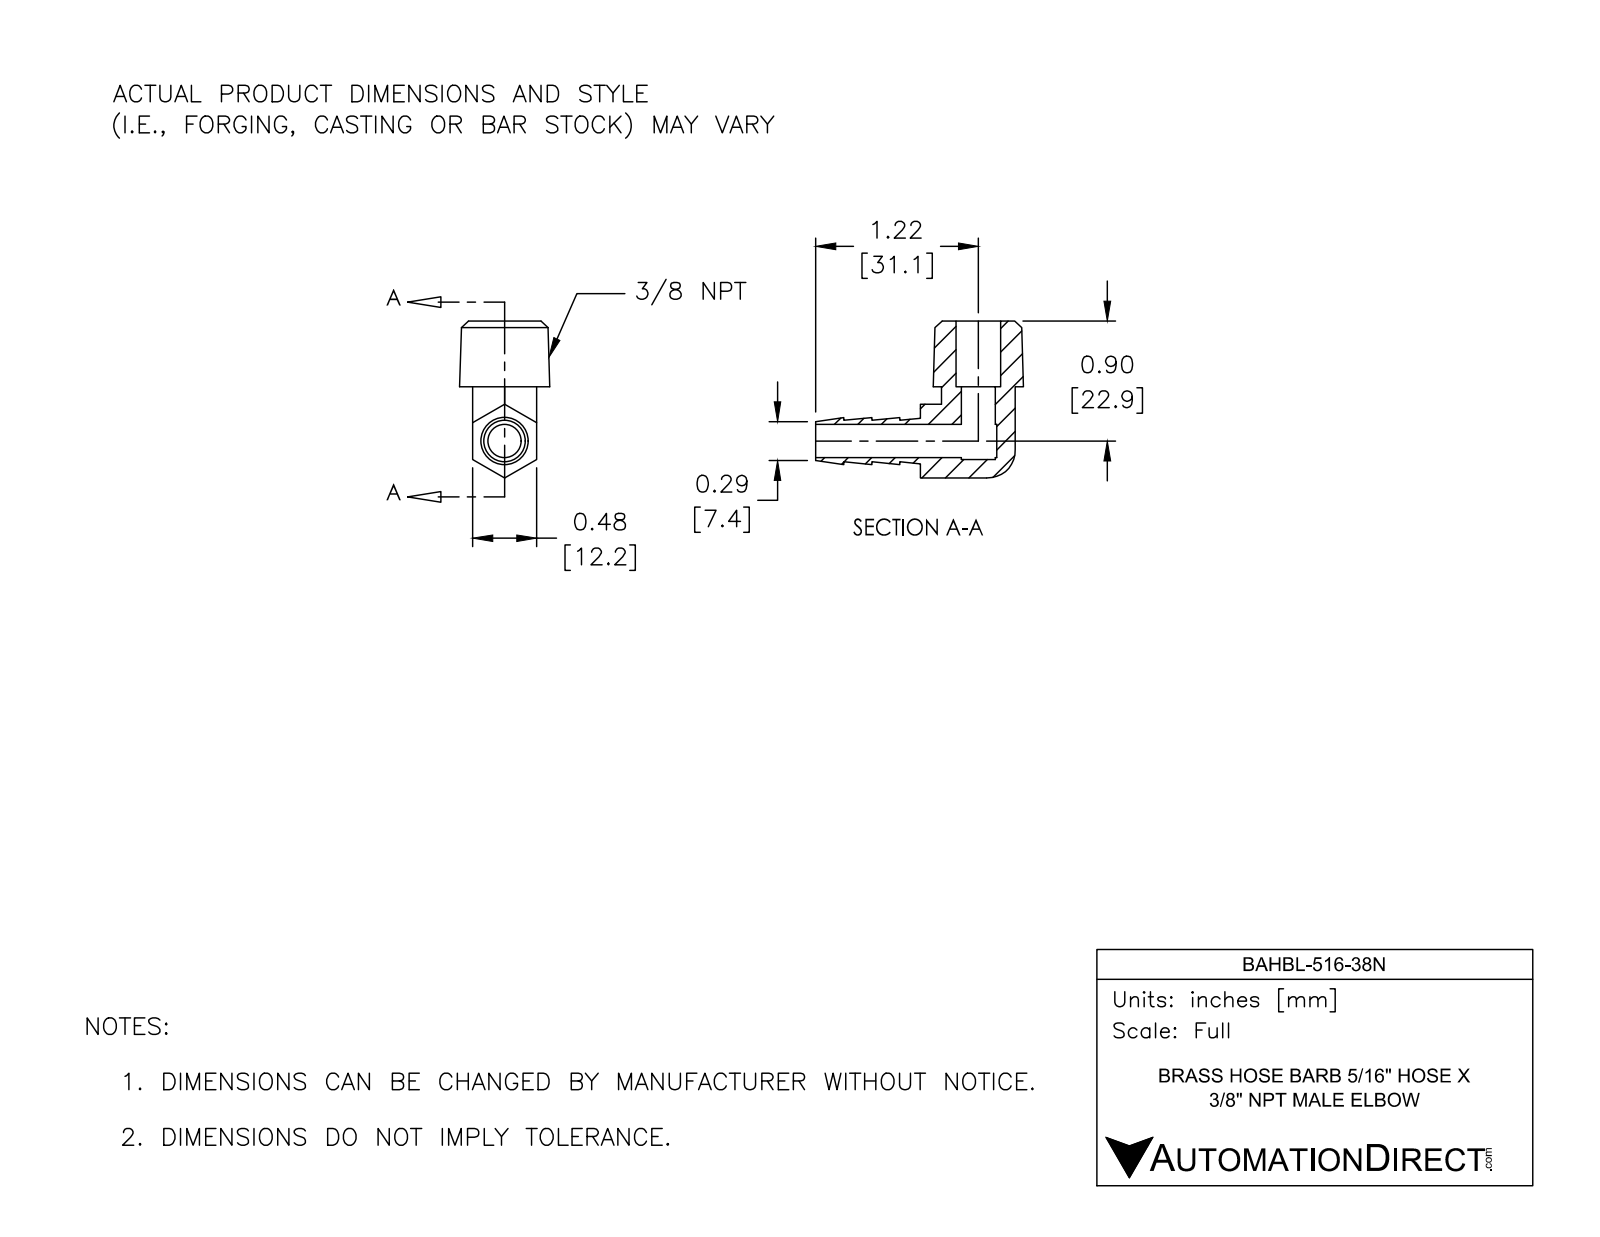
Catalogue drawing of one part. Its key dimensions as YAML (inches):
part_name: "BAHBL-516-38N"
step_written_by: "SolidWorks 2017 (AUTOMOTIVE_DESIGN)"
units: inches
bodies: {solids: 1, faces: 42, planar: 20, cylindrical: 10, other: 12}
overall_size: [1.563, 1.181, 0.679]
volume: 0.274
surface_area: 5.666
round_holes:
  - {diameter: 0.25, count: 1}
  - {diameter: 0.255, count: 1}
  - {diameter: 0.336, count: 1}
partial_cylinders:
  - {radius: 0.25, count: 2}
face_to_face_distances: [0.481, 0.495, 0.211, 0.547, 1.042, 0.575, 0.422, 1.362, 0.787, 0.729]
